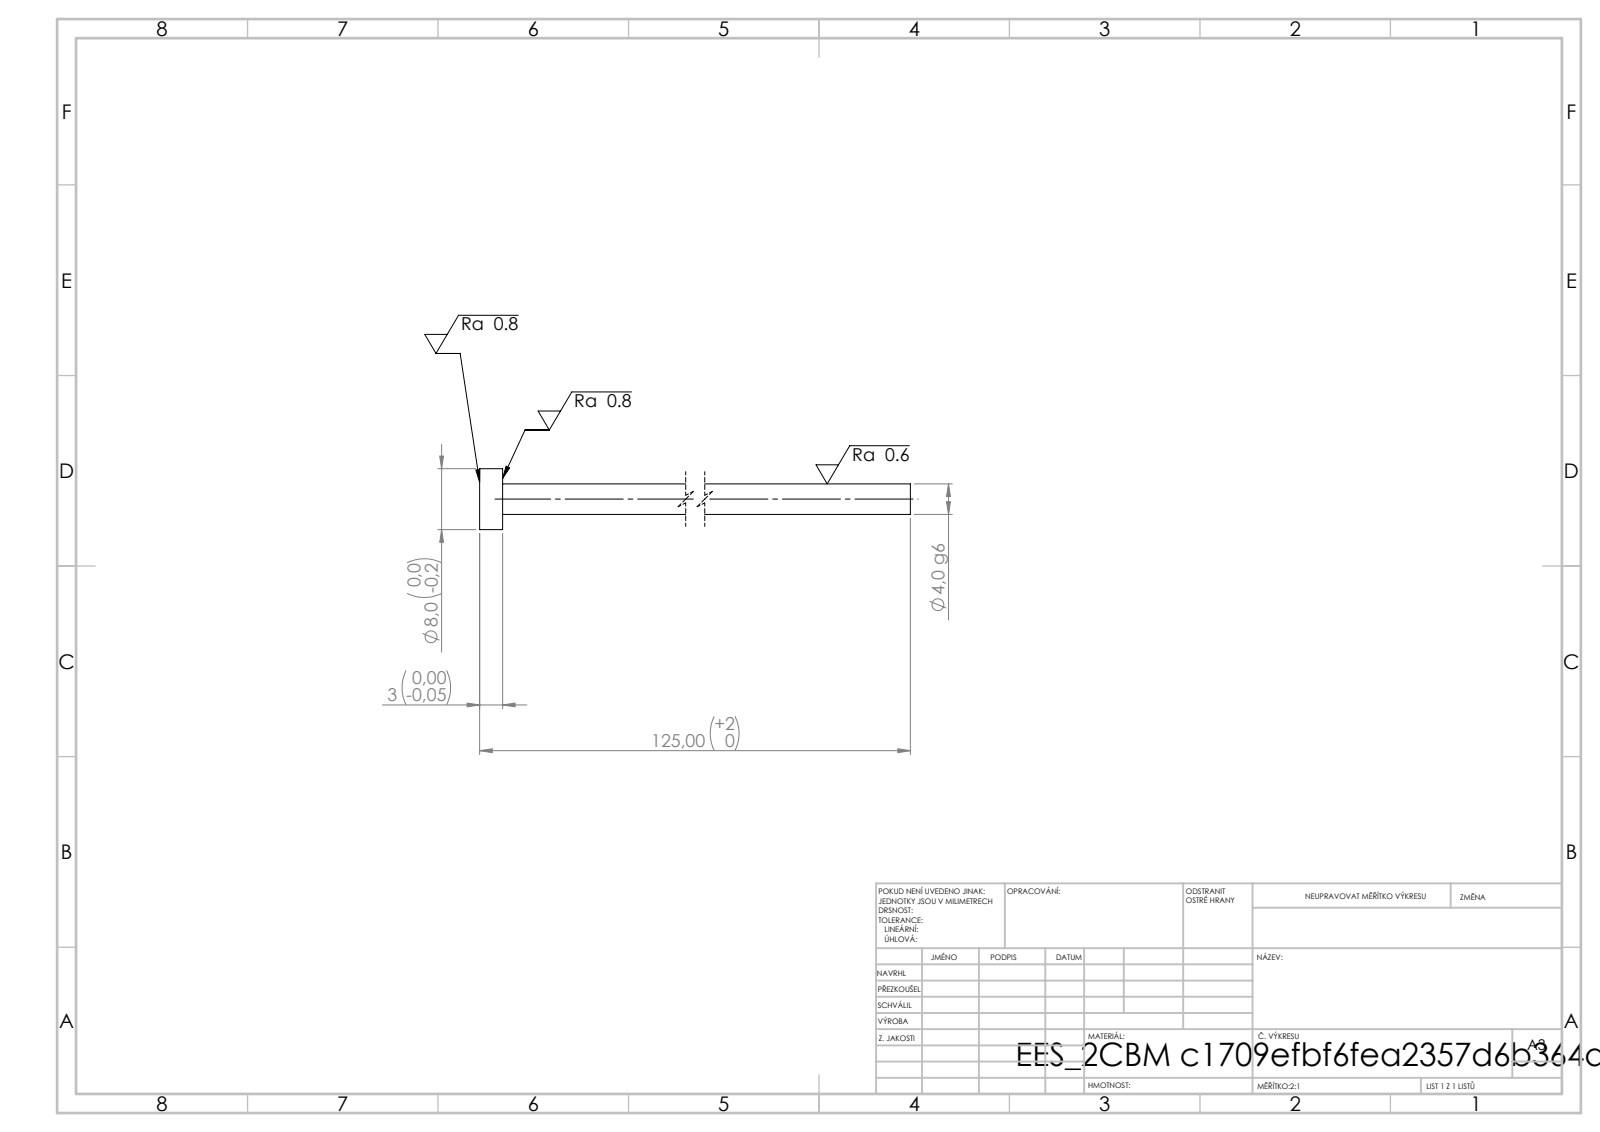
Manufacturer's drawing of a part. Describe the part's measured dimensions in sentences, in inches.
Its 3-D file was written by "SolidWorks 2019 (CONFIG_CONTROL_DESIGN)". It is 1 solid with 7 faces: 3 planar, 4 cylindrical and 0 other. Overall it measures 4.921 by 0.315 by 0.315 inches. Its volume is 0.103 cubic inches and its surface area 2.649 square inches. Round bosses or shafts: 1 of diameter 0.315, 1 of diameter 0.157. The main face-to-face distances are 0.118, 4.921, 4.803.
